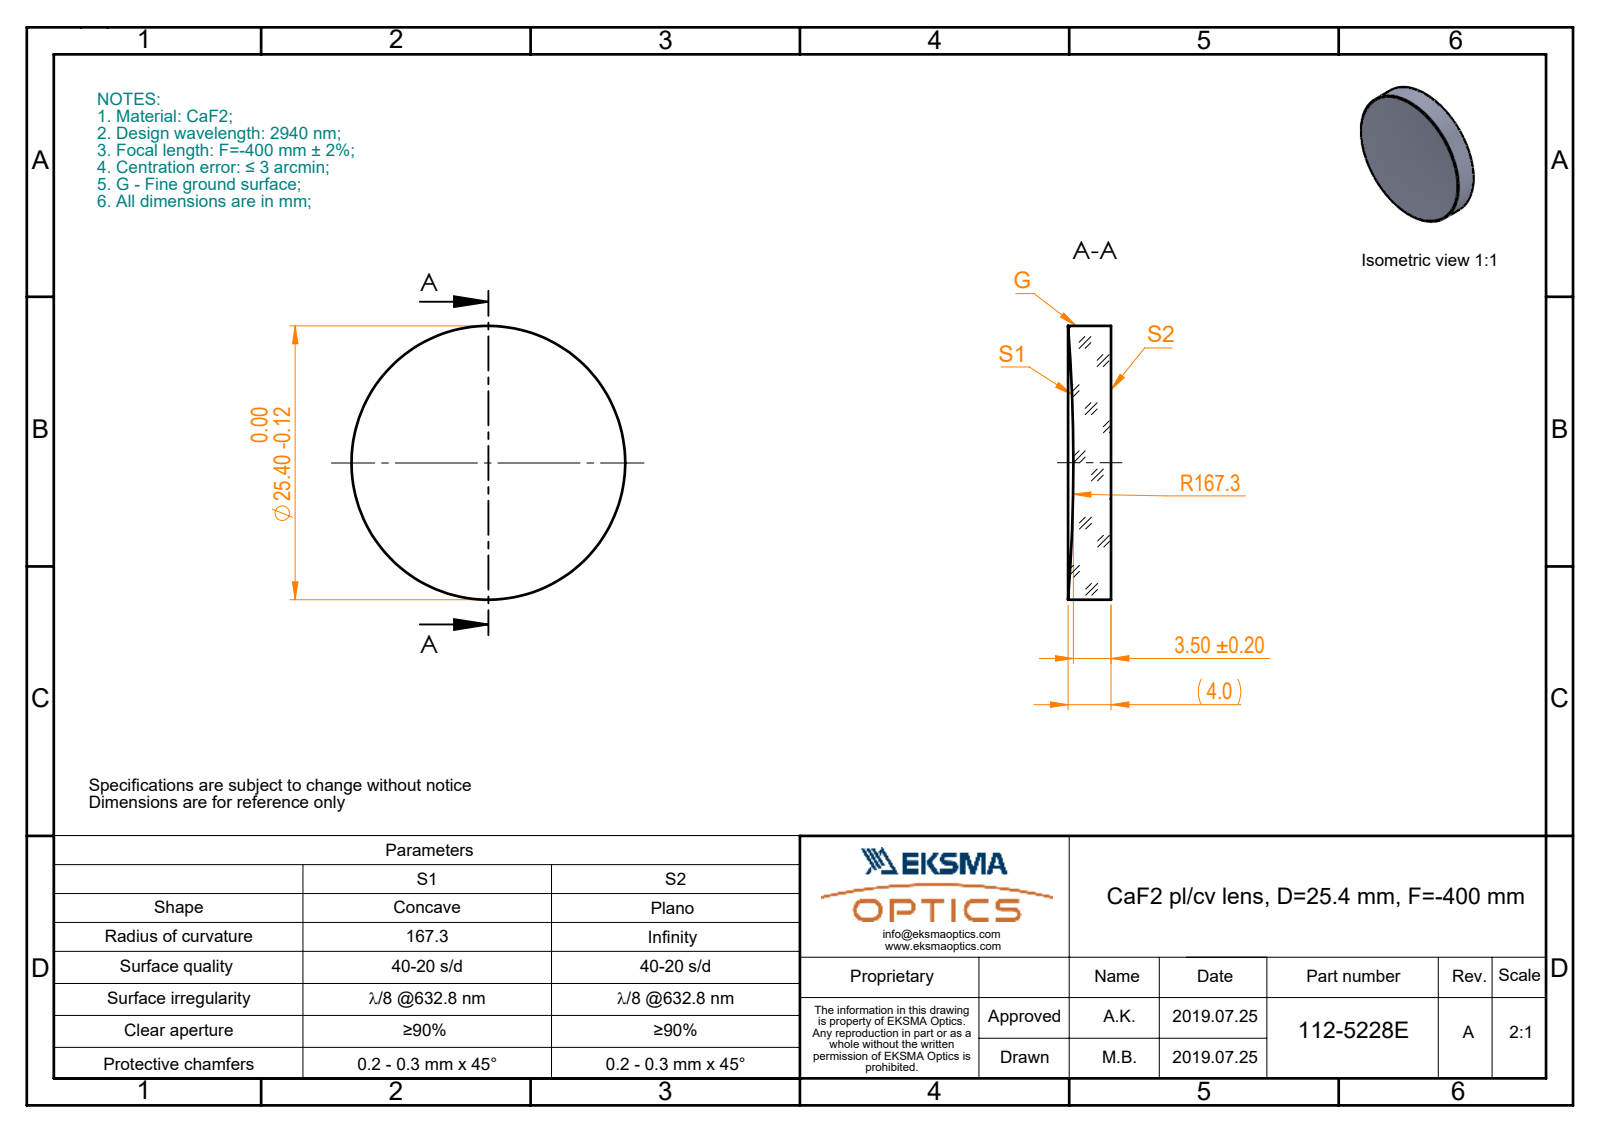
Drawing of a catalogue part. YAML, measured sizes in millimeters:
part_name: "112-5228E CaF2 pl-cv 25.4 F-400"
step_written_by: "SolidWorks 2017 (CONFIG_CONTROL_DESIGN)"
units: millimeters
bodies: {solids: 1, faces: 5, planar: 1, cylindrical: 2, other: 2}
overall_size: [25.4, 25.4, 3.98]
volume: 1896
surface_area: 1332
round_bosses_or_shafts:
  - {diameter: 25.4, count: 1}
